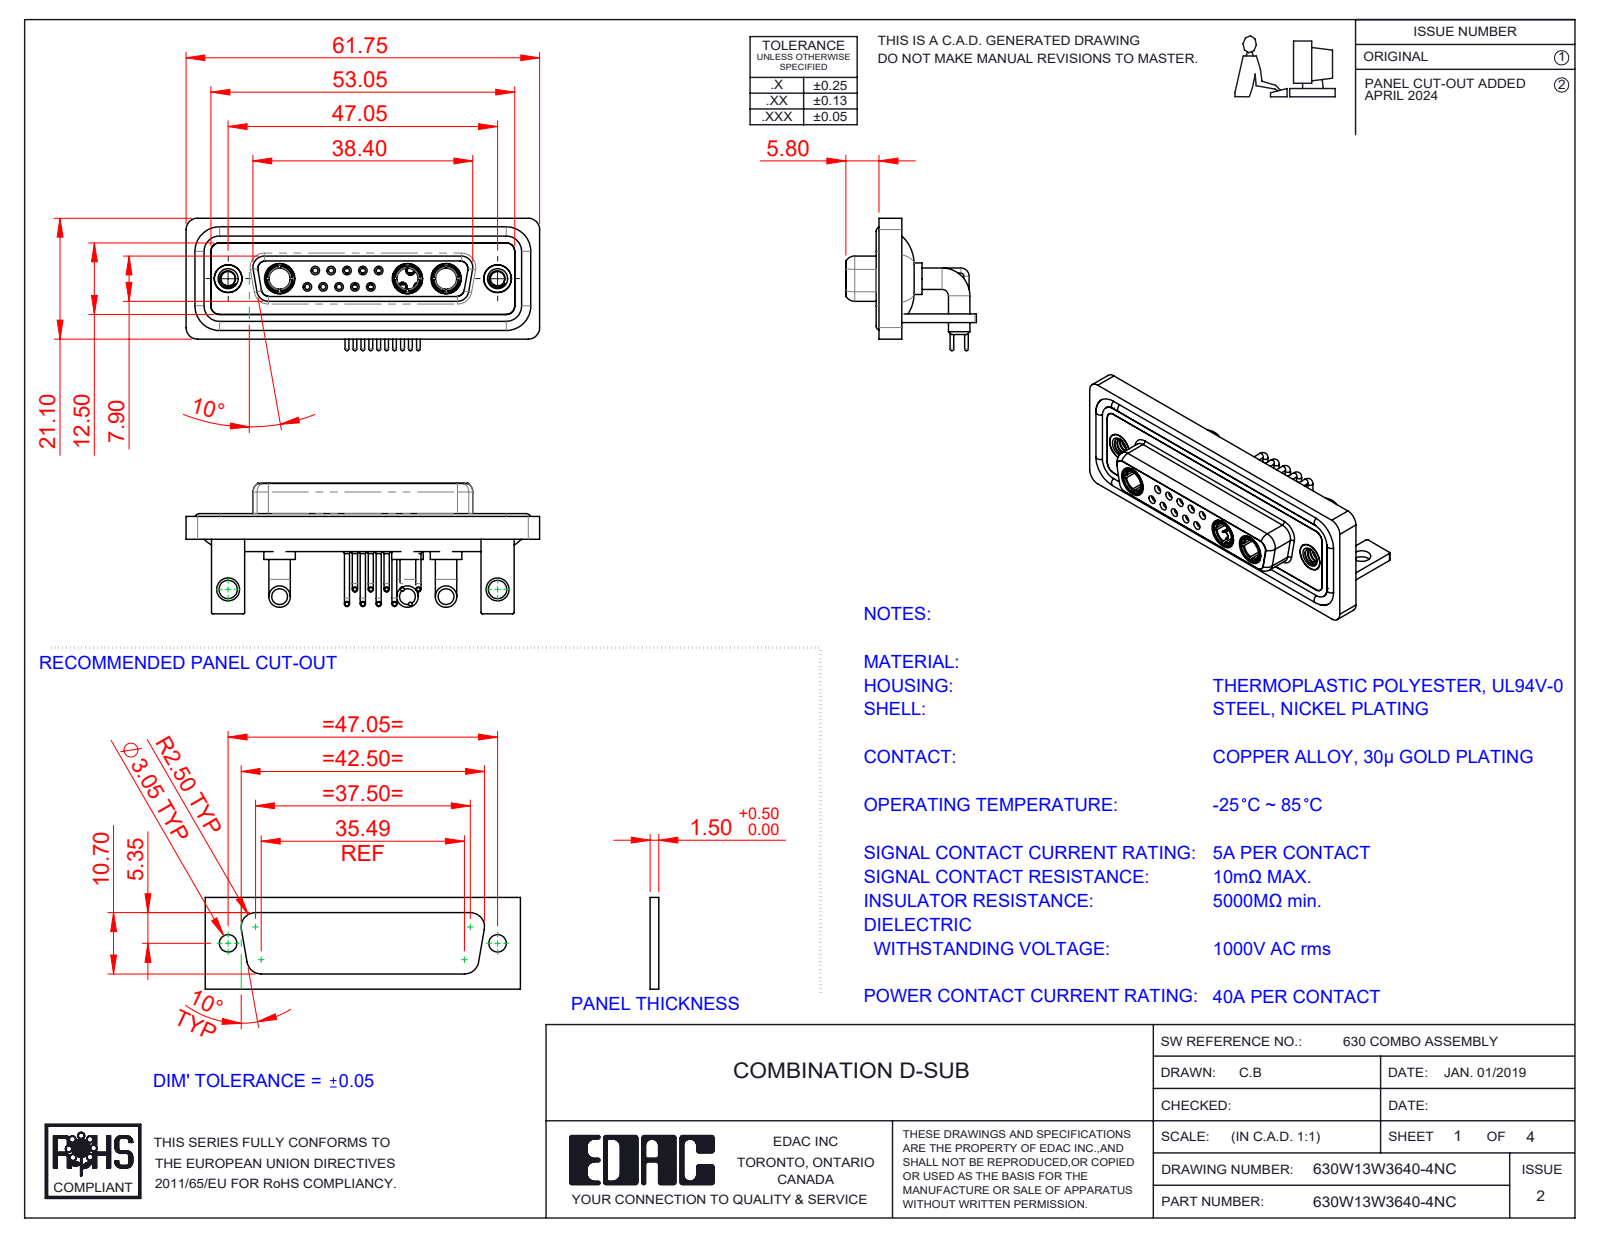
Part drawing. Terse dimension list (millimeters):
name: 630Combo Waterproof Housing_25 Contacts; Power Socket_40A RA; 630Combo Threaded Rivet_A; 630Combo Housing_13W3 (+6 more)
written by: SolidWorks 2023 (CONFIG_CONTROL_DESIGN)
unit: mm
bodies: 25 solids, 1192 faces (362 planar, 515 cylindrical, 315 other)
size: 61.75 × 23.12 × 22.8
volume: 9 048 mm³; area: 15 166 mm²
holes: 10× ⌀0.9, 10× ⌀1.1, 10× ⌀1.5, 10× ⌀2, 5× ⌀1.6, 5× ⌀1.7, 5× ⌀4.85, 3× ⌀3.7, 3× ⌀5.3, 2× ⌀2.5, 2× ⌀3.2, 2× ⌀4
bosses: 15× ⌀0.9, 12× ⌀1.6, 10× ⌀0.65, 6× ⌀3.75, 5× ⌀2, 5× ⌀1.5, 3× ⌀5.5, 3× ⌀5.2
rounds: 19× R2, 18× R1.5, 16× R0.25, 8× R1.35, 8× R1.6, 5× R0.5, 4× R0.6, 4× R0.65
face distances: 0.4, 1.8, 2.9, 3.7, 1.5, 4.1, 1.1, 1.4, 1.6, 3.1
hole spacings: 3.16, 2.77, 5.54, 5.04, 8.31, 5.03, 7.49, 11.08
